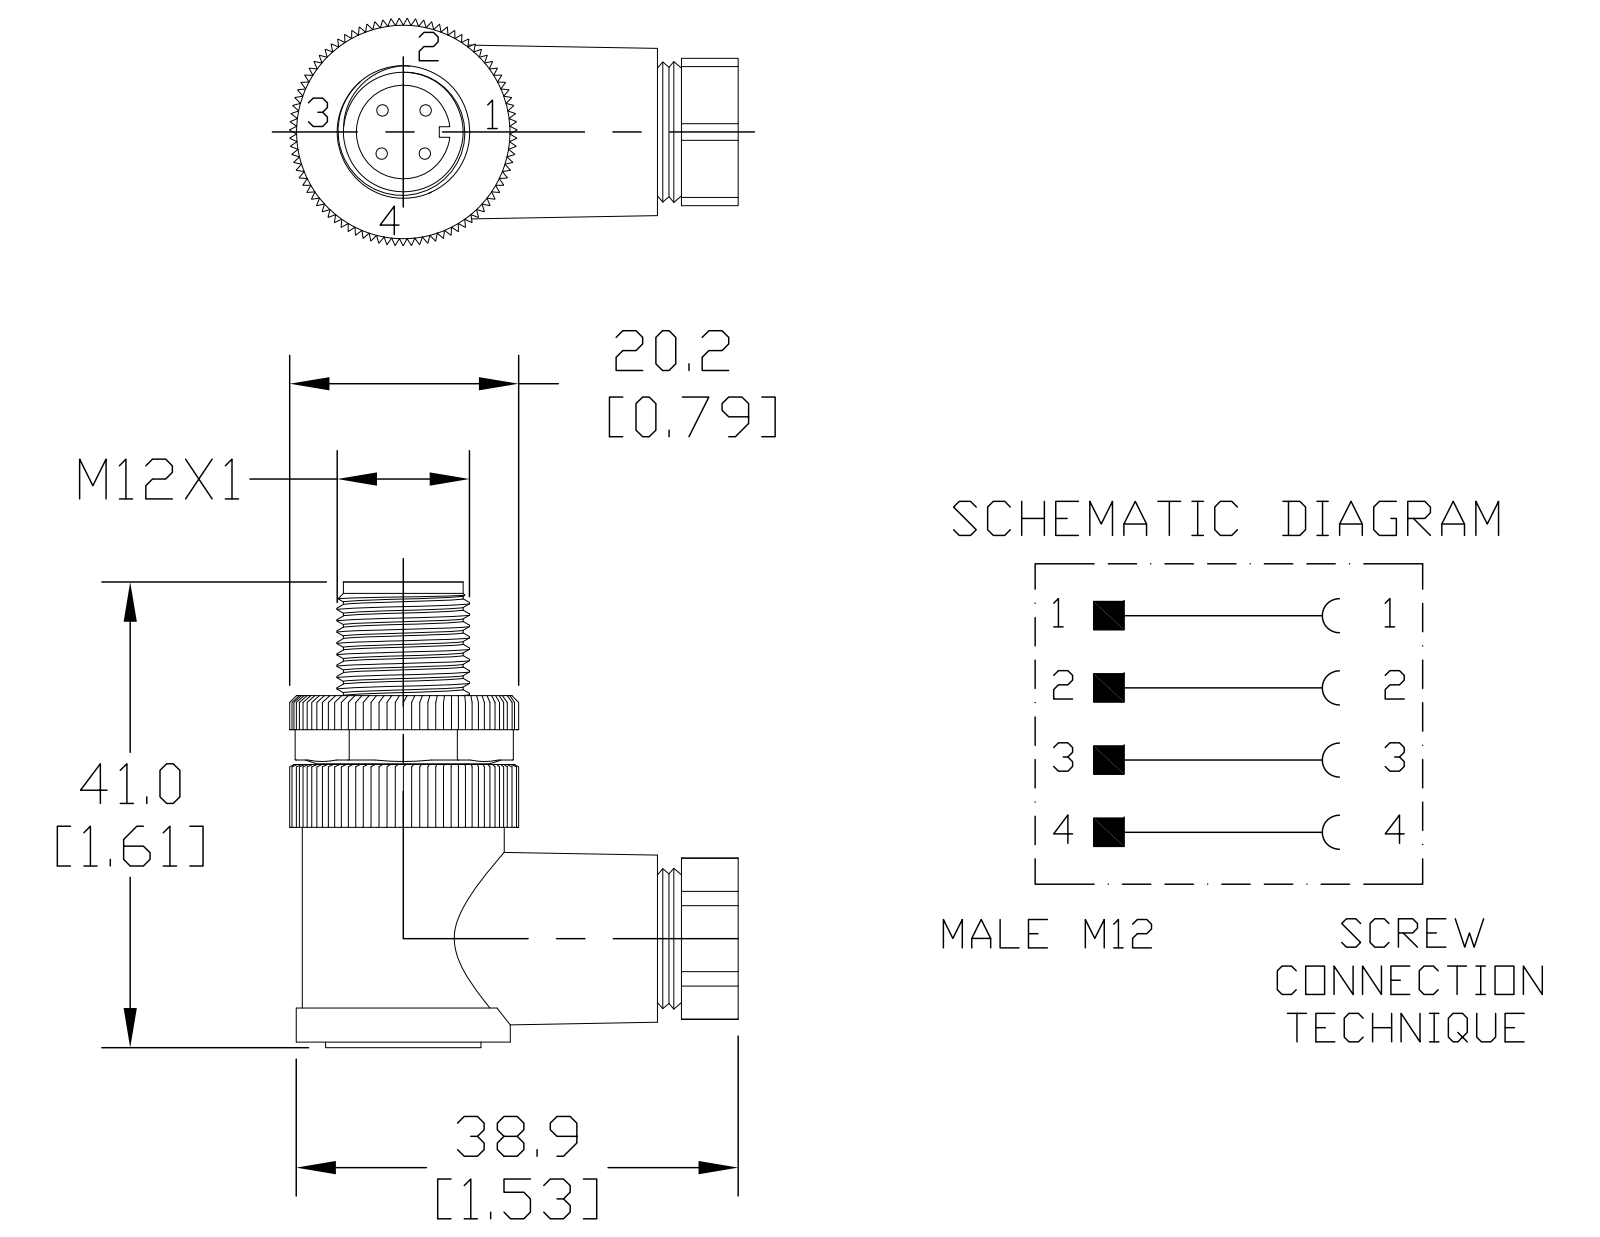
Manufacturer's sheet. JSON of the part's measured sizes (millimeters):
{"part_name": "7000-12821-0000000", "step_written_by": "SolidWorks 2015 (AUTOMOTIVE_DESIGN)", "units": "millimeters", "bodies": {"solids": 1, "faces": 822, "planar": 397, "cylindrical": 225, "other": 200}, "overall_size": [41, 39.5, 19.99], "volume_mm3": 11554, "surface_area_mm2": 5786, "round_holes": [[6.85, 1], [8.25, 1], [13.13, 1]], "round_bosses_or_shafts": [[1, 4], [18.86, 1], [17.78, 1], [13.68, 1], [11.68, 1], [11.07, 1], [10.54, 1]], "partial_cylinders_radius": [[7.11, 1], [10, 1]], "face_to_face_distances": [30.5, 24.43, 6.07, 3, 24.5, 5, 12.98, 6, 27.5, 16.5]}
